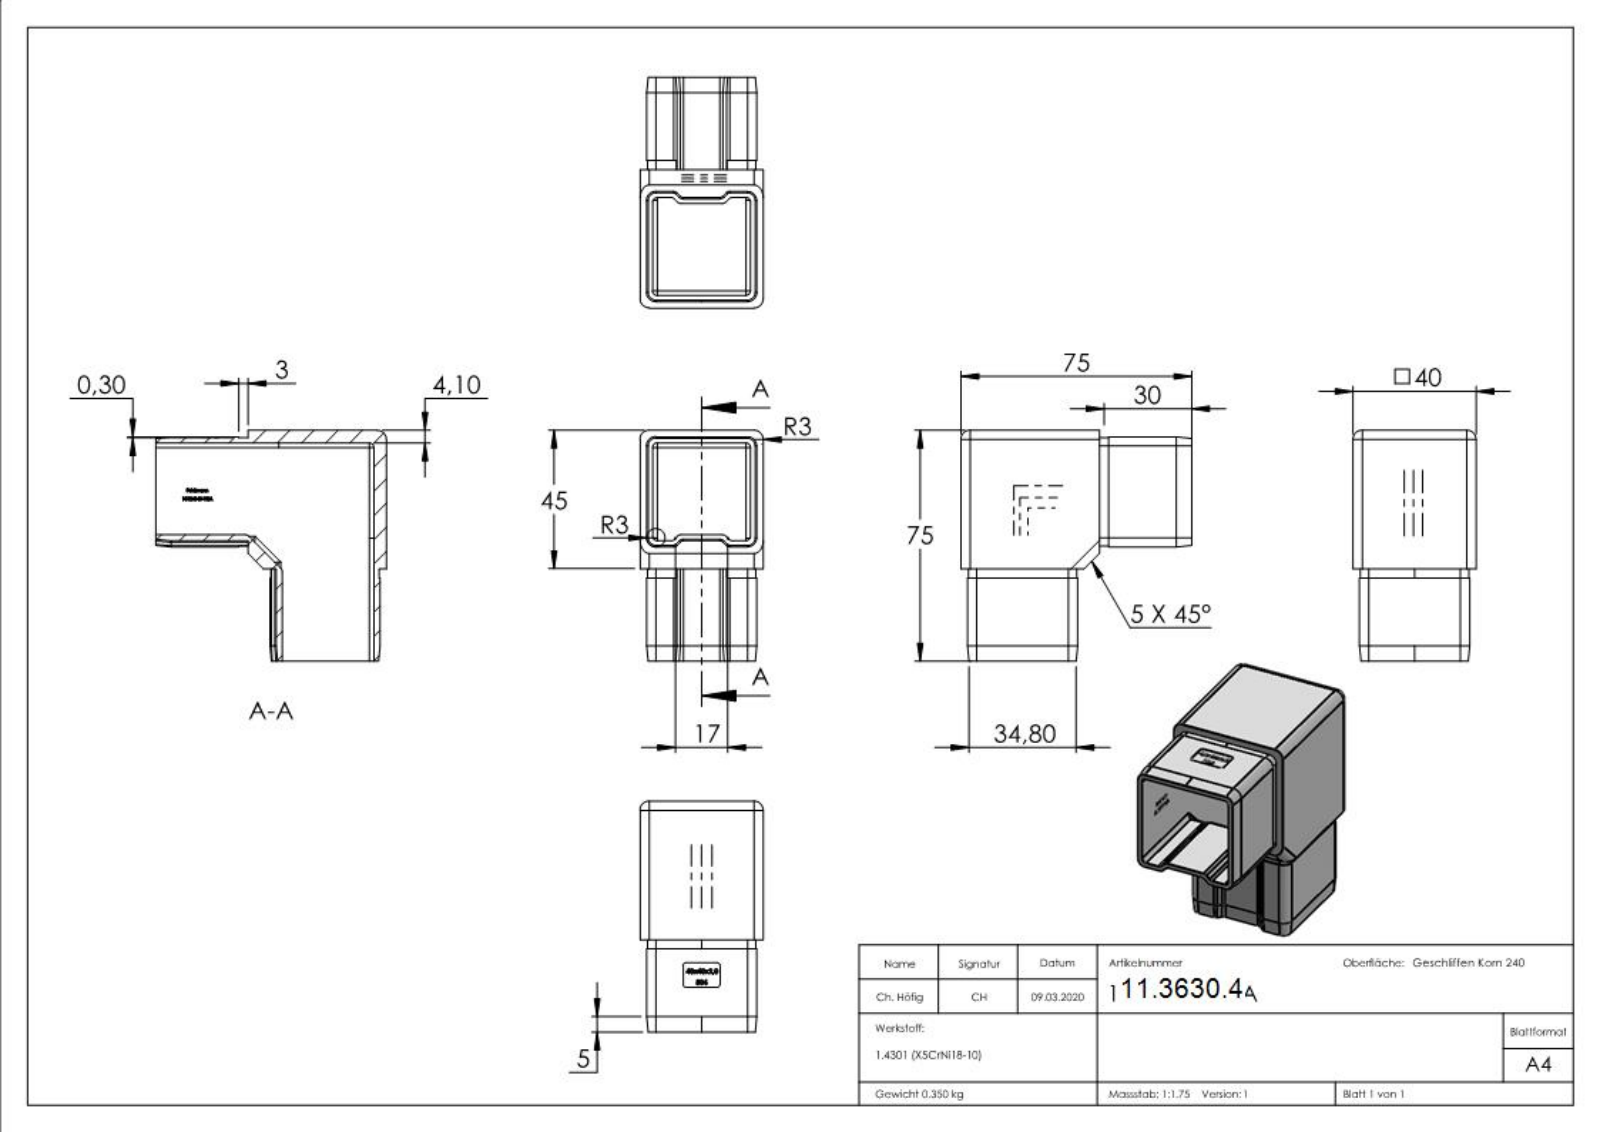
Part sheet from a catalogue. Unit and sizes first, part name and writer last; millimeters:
Units: millimetres
Overall size (bounding box): 75 × 75 × 40
Partial cylindrical surfaces — rounded edges, fillets, slot ends (radius × count): R1.5 ×35, R3 ×15, R2.7 ×8, R1 ×4
Main face-to-face distances: 4.1, 2, 31.8, 35.9, 33.8, 2.1, 37.9, 35.8, 40, 33.9
Volume: 44 273 mm³ · Surface area: 30 927 mm²
Bodies: 1 solid, 595 faces (349 planar, 68 cylindrical, 178 other)
Part name (STEP PRODUCT): 10124040-V2A
STEP written by: SolidWorks 2015 (CONFIG_CONTROL_DESIGN)
